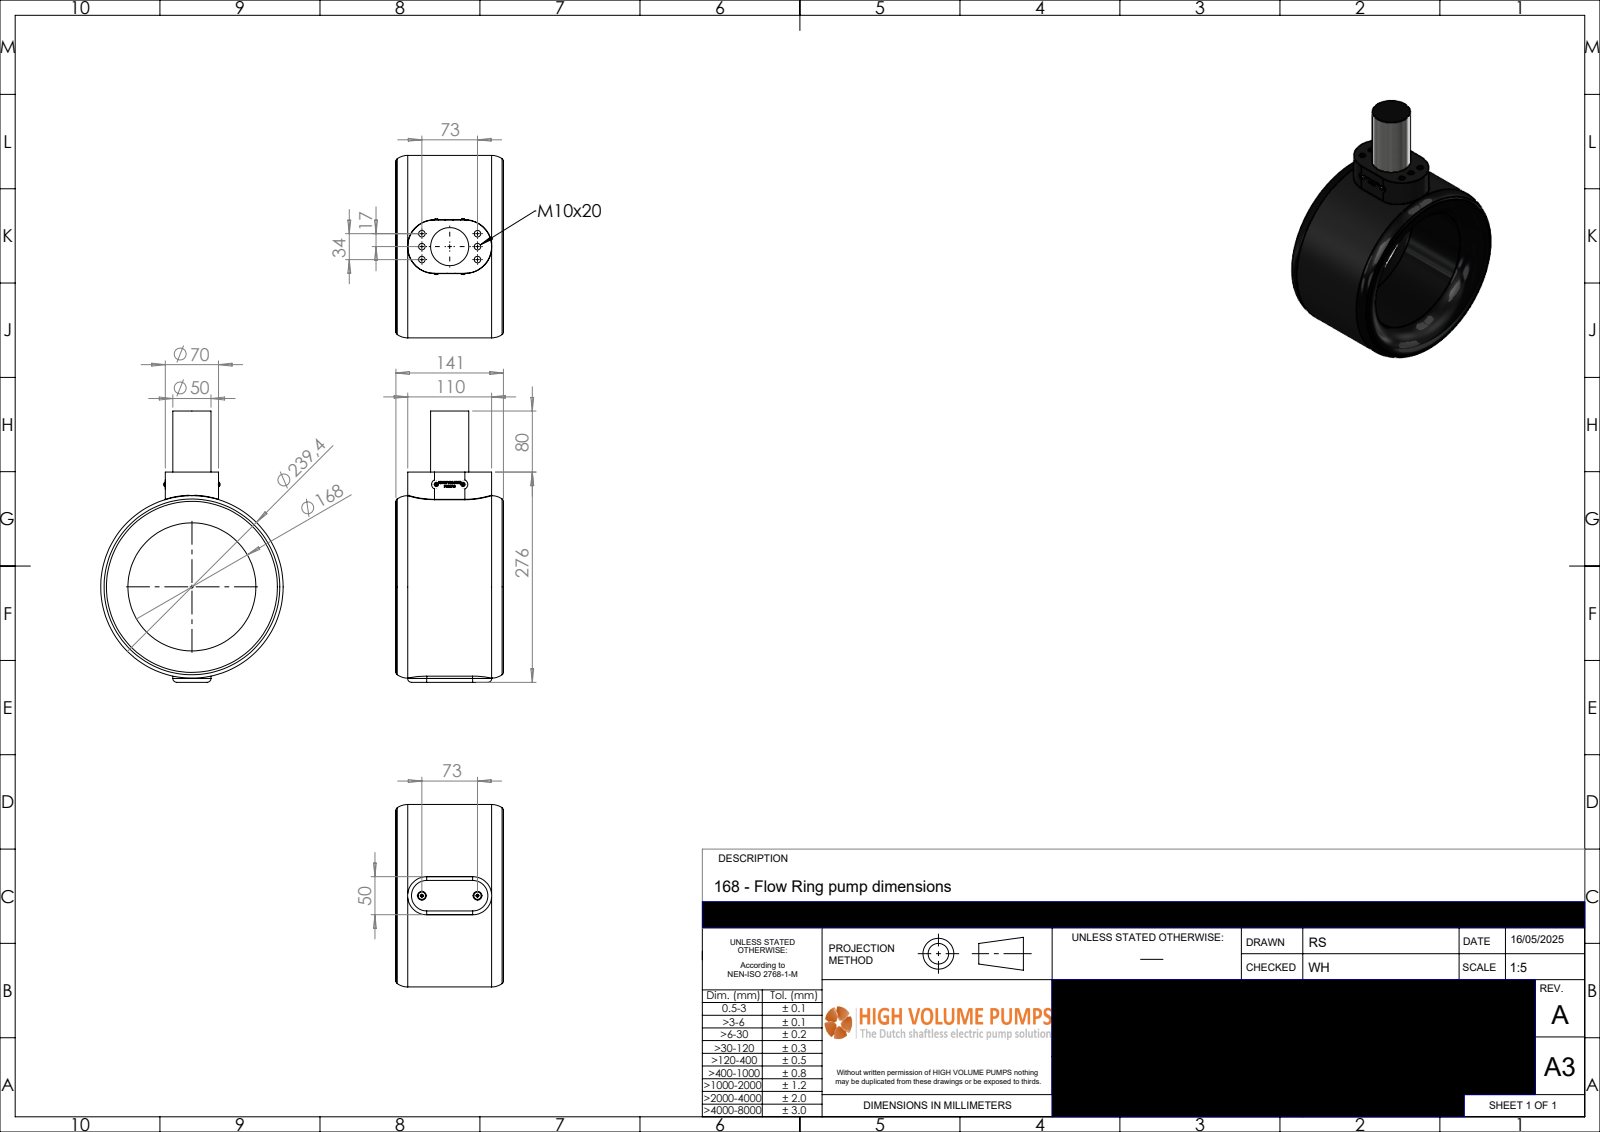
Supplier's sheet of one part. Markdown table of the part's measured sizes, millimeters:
| quantity | value |
| --- | --- |
| part name | P-168-030-rev-A-FR |
| STEP written by | SolidWorks 2024 (AUTOMOTIVE_DESIGN) |
| units | millimeters |
| bodies | 2 solids, 615 faces (395 planar, 50 cylindrical, 170 other) |
| overall size | 355.85 × 239.4 × 141.11 |
| volume | 3 399 000 mm³ |
| surface area | 245 756 mm² |
| round holes (diameter × count) | 8.5 × 6, 3.5 × 2, 5.3 × 2, 168 × 1 |
| round bosses / shafts (diameter × count) | 9.64 × 6, 5.7 × 2, 5 × 2, 3 × 2, 239.4 × 1, 50 × 1 |
| partial cylindrical surfaces (radius × count) | 0.5 × 2, 5 × 2, 6.35 × 2, 25 × 2, 35 × 2 |
| main face-to-face distances | 270.84, 5, 275.84, 355.84, 350.84, 80, 70, 0.43, 10, 60 |
| hole center spacings | 17, 74.95, 73, 34, 80.53, 35 |
